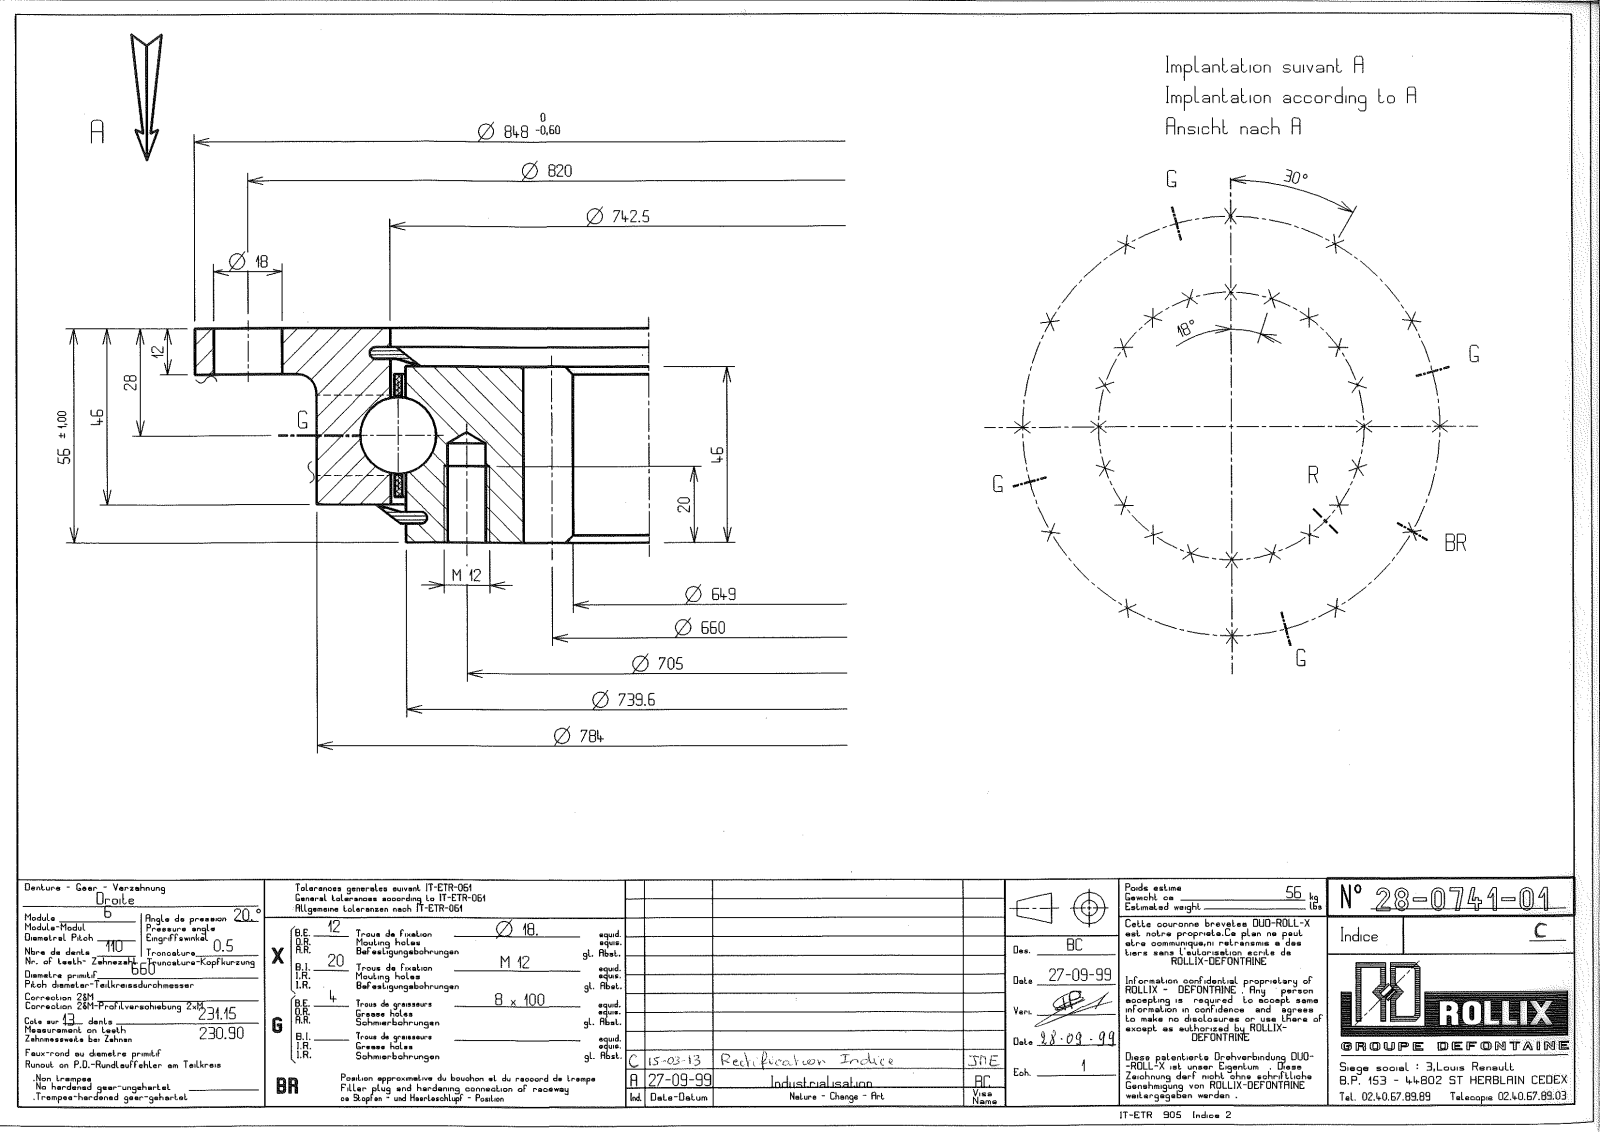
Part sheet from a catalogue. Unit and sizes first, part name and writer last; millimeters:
Units: millimetres
Overall size (bounding box): 848 × 848 × 56
Round holes (diameter × count): ⌀10.25 ×20, ⌀18 ×12, ⌀7 ×4, ⌀745.5 ×1
Round bosses / shafts (diameter × count): ⌀8 ×4, ⌀848 ×1, ⌀784 ×1, ⌀736.5 ×1
Partial cylindrical surfaces — rounded edges, fillets, slot ends (radius × count): R324.5 ×1, R337.5 ×1
Main face-to-face distances: 10, 46, 56, 44, 2, 12, 34, 36, 4.95, 51.05
Hole centre spacings: 498.51, 570.36, 696.32, 414.39, 628.16, 110.29, 217.86, 320.06
Volume: 6 432 000 mm³ · Surface area: 1 167 000 mm²
Bodies: 9 solids, 920 faces (273 planar, 317 cylindrical, 330 other)
Part name (STEP PRODUCT): 22-0741-01
STEP written by: SolidWorks 2016 (CONFIG_CONTROL_DESIGN)
